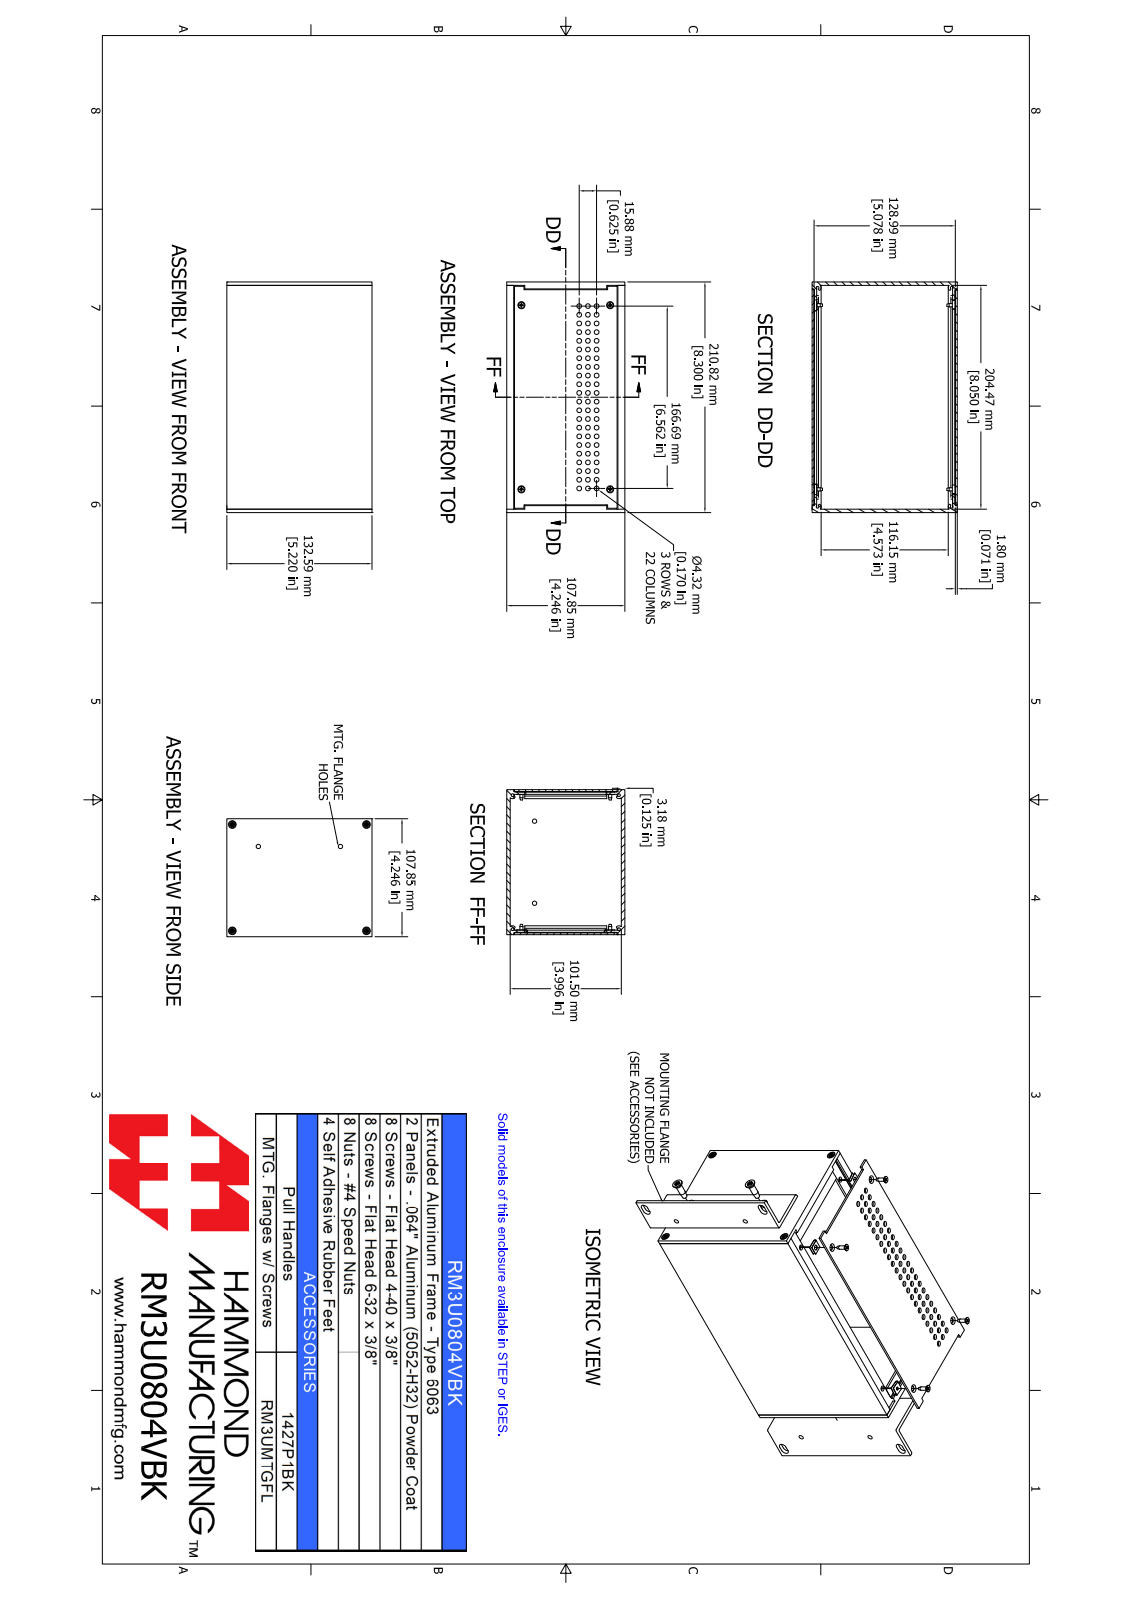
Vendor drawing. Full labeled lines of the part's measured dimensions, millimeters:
Part name (STEP PRODUCT): RM3U0804VBK
STEP written by: SolidWorks 2021 (AUTOMOTIVE_DESIGN)
Units: millimetres
Bodies: 30 solids, 936 faces (396 planar, 252 cylindrical, 288 other)
Overall size (bounding box): 210.8 × 132.6 × 107.8
Volume: 376 200 mm³ · Surface area: 292 500 mm²
Round holes (diameter × count): ⌀4.3 ×66, ⌀2.5 ×4, ⌀3.5 ×4, ⌀4 ×4, ⌀4.3 ×4, ⌀4 ×2
Round bosses / shafts (diameter × count): ⌀6 ×4, ⌀5.4 ×4, ⌀3.5 ×4, ⌀2.8 ×4
Partial cylindrical surfaces — rounded edges, fillets, slot ends (radius × count): R0.9 ×8, R1 ×8, R1.2 ×8, R1.3 ×8, R3.2 ×8, R1 ×4
Main face-to-face distances: 3.2, 3.2, 1.8, 130.8, 107.8, 101.5, 104.7, 104.7, 132.6, 129
Hole centre spacings: 17.8, 8, 15.9, 25.1, 32.7, 11.2, 7.9, 23.8
